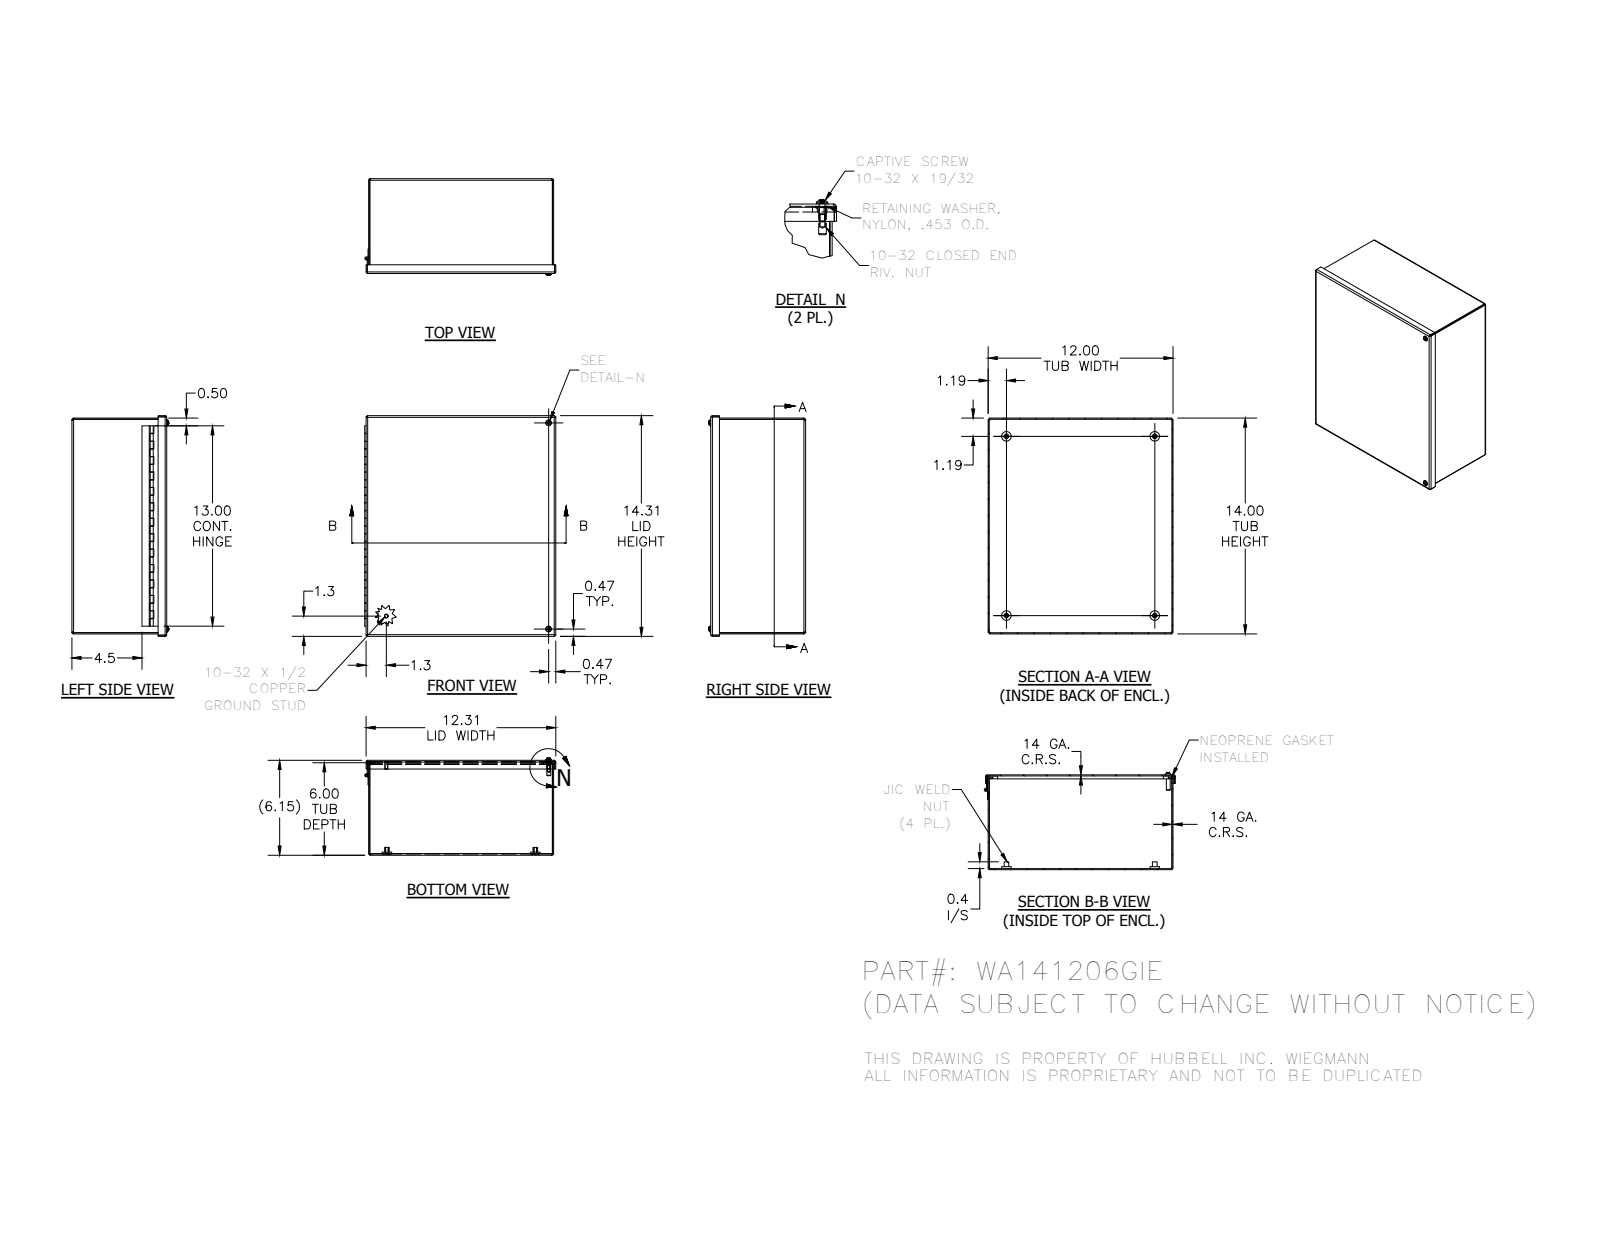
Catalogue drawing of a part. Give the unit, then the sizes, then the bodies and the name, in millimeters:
Units: millimetres
Overall size (bounding box): 363.54 × 314.88 × 159.56
Round holes (diameter × count): ⌀3.96 ×6, ⌀6.53 ×4, ⌀7.94 ×4, ⌀4.98 ×2, ⌀7.06 ×2, ⌀7.14 ×2, ⌀2.96 ×1
Round bosses / shafts (diameter × count): ⌀15.88 ×4, ⌀7.62 ×4, ⌀4.83 ×3, ⌀11.51 ×2, ⌀10.31 ×2, ⌀9.47 ×2, ⌀6.3 ×2, ⌀6.35 ×1
Partial cylindrical surfaces — rounded edges, fillets, slot ends (radius × count): R0.79 ×12, R2.67 ×12, R1.78 ×8, R2.27 ×2
Main face-to-face distances: 1.88, 154.38, 152.5, 156.26, 302.92, 353.72, 301.04, 304.8, 355.6, 351.84
Hole centre spacings: 339.72, 31.42, 267.62, 288.92, 445.96, 339.71, 289.21, 318.28
Volume: 964 312 mm³ · Surface area: 989 630 mm²
Bodies: 18 solids, 505 faces (293 planar, 137 cylindrical, 75 other)
Part name (STEP PRODUCT): WA141206GIEBKP; 3499; 328124LH; 328124P (+8 more)
STEP written by: Autodesk Inventor 2014 (AUTOMOTIVE_DESIGN)
